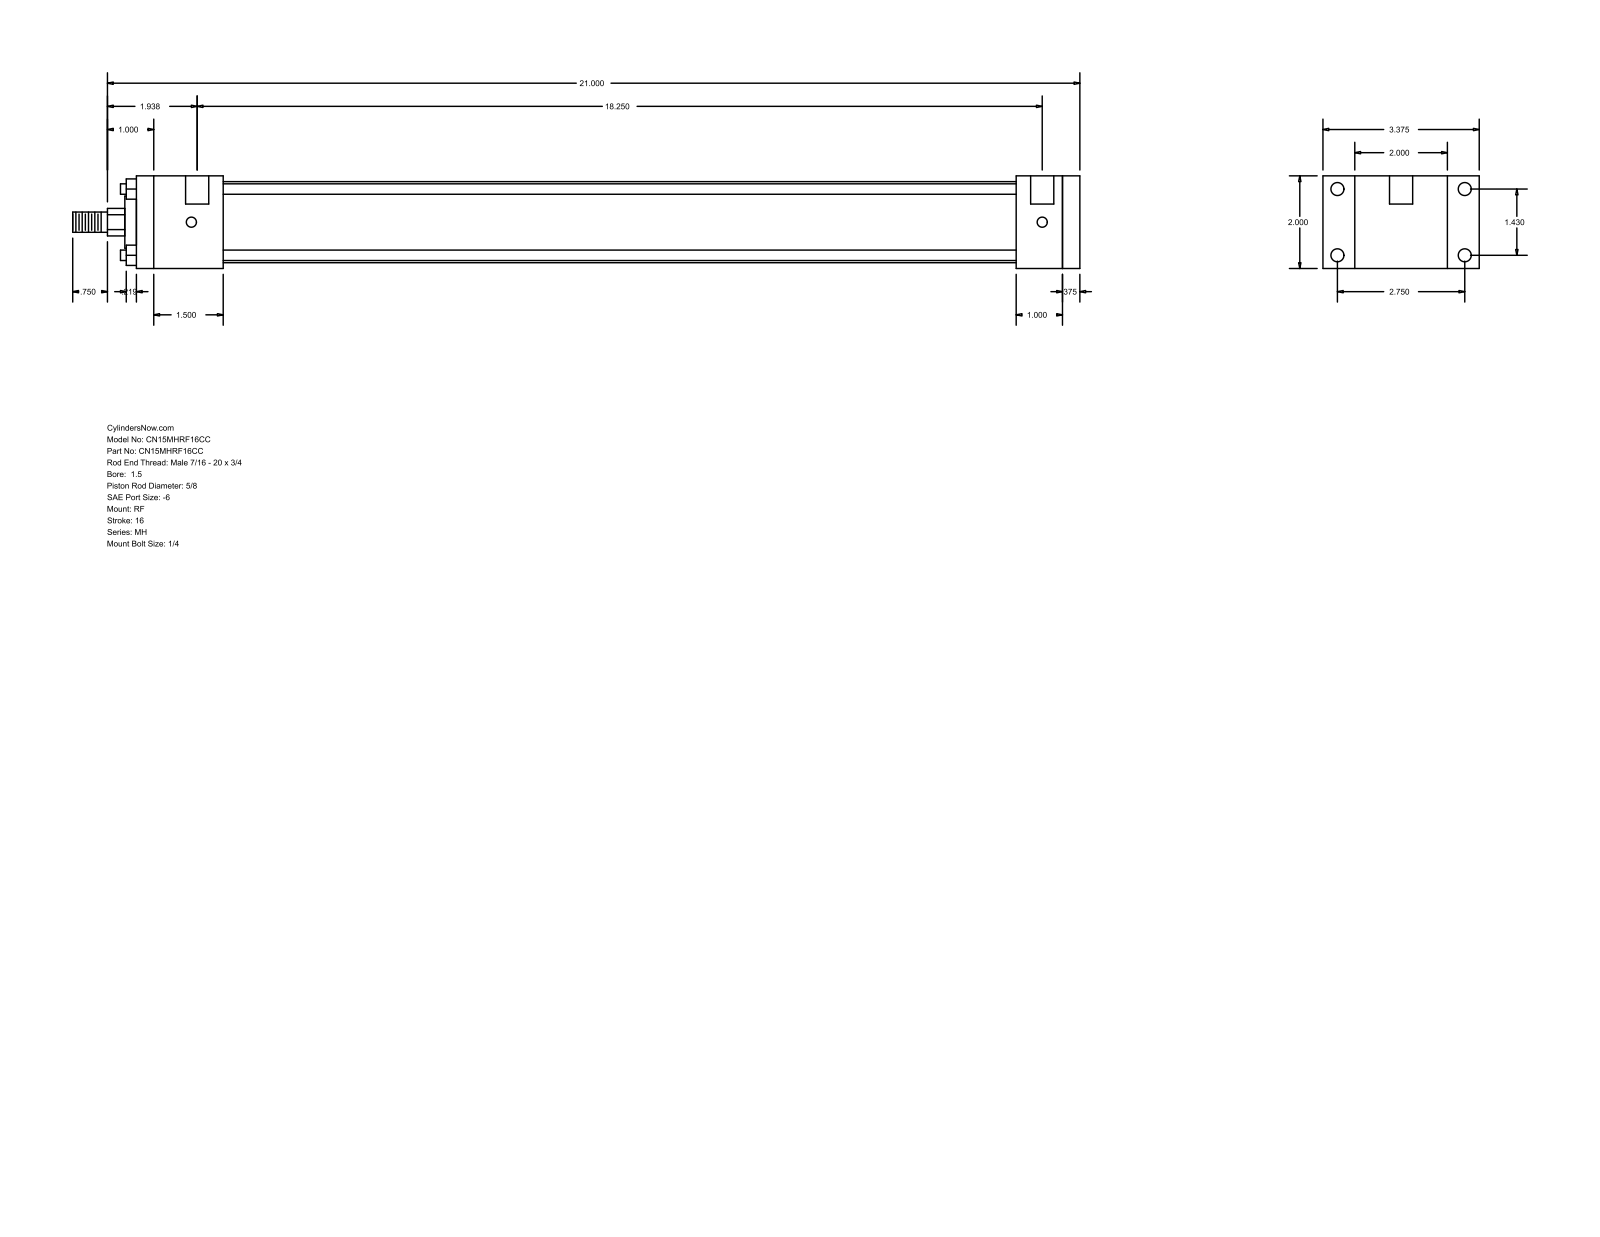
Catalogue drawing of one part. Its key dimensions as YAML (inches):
part_name: "MH_RF__0150_0.625"
step_written_by: "GSSL Pune (CONFIG_CONTROL_DESIGN)"
units: inches
bodies: {solids: 0, faces: 92, planar: 64, cylindrical: 28, other: 0}
overall_size: [21.75, 3.375, 2]
round_holes:
  - {diameter: 0.219, count: 4}
  - {diameter: 0.281, count: 4}
  - {diameter: 0.5, count: 2}
round_bosses_or_shafts:
  - {diameter: 0.225, count: 4}
  - {diameter: 1.75, count: 1}
  - {diameter: 1.125, count: 1}
  - {diameter: 0.625, count: 1}
  - {diameter: 0.437, count: 1}
partial_cylinders:
  - {radius: 0.297, count: 1}
face_to_face_distances: [2, 0.375, 20, 20.375, 1, 0.687, 2.687, 19, 1.375, 1.875]
hole_center_spacings: [1.43, 2.75, 3.099, 18.375, 0.125, 18.25]
